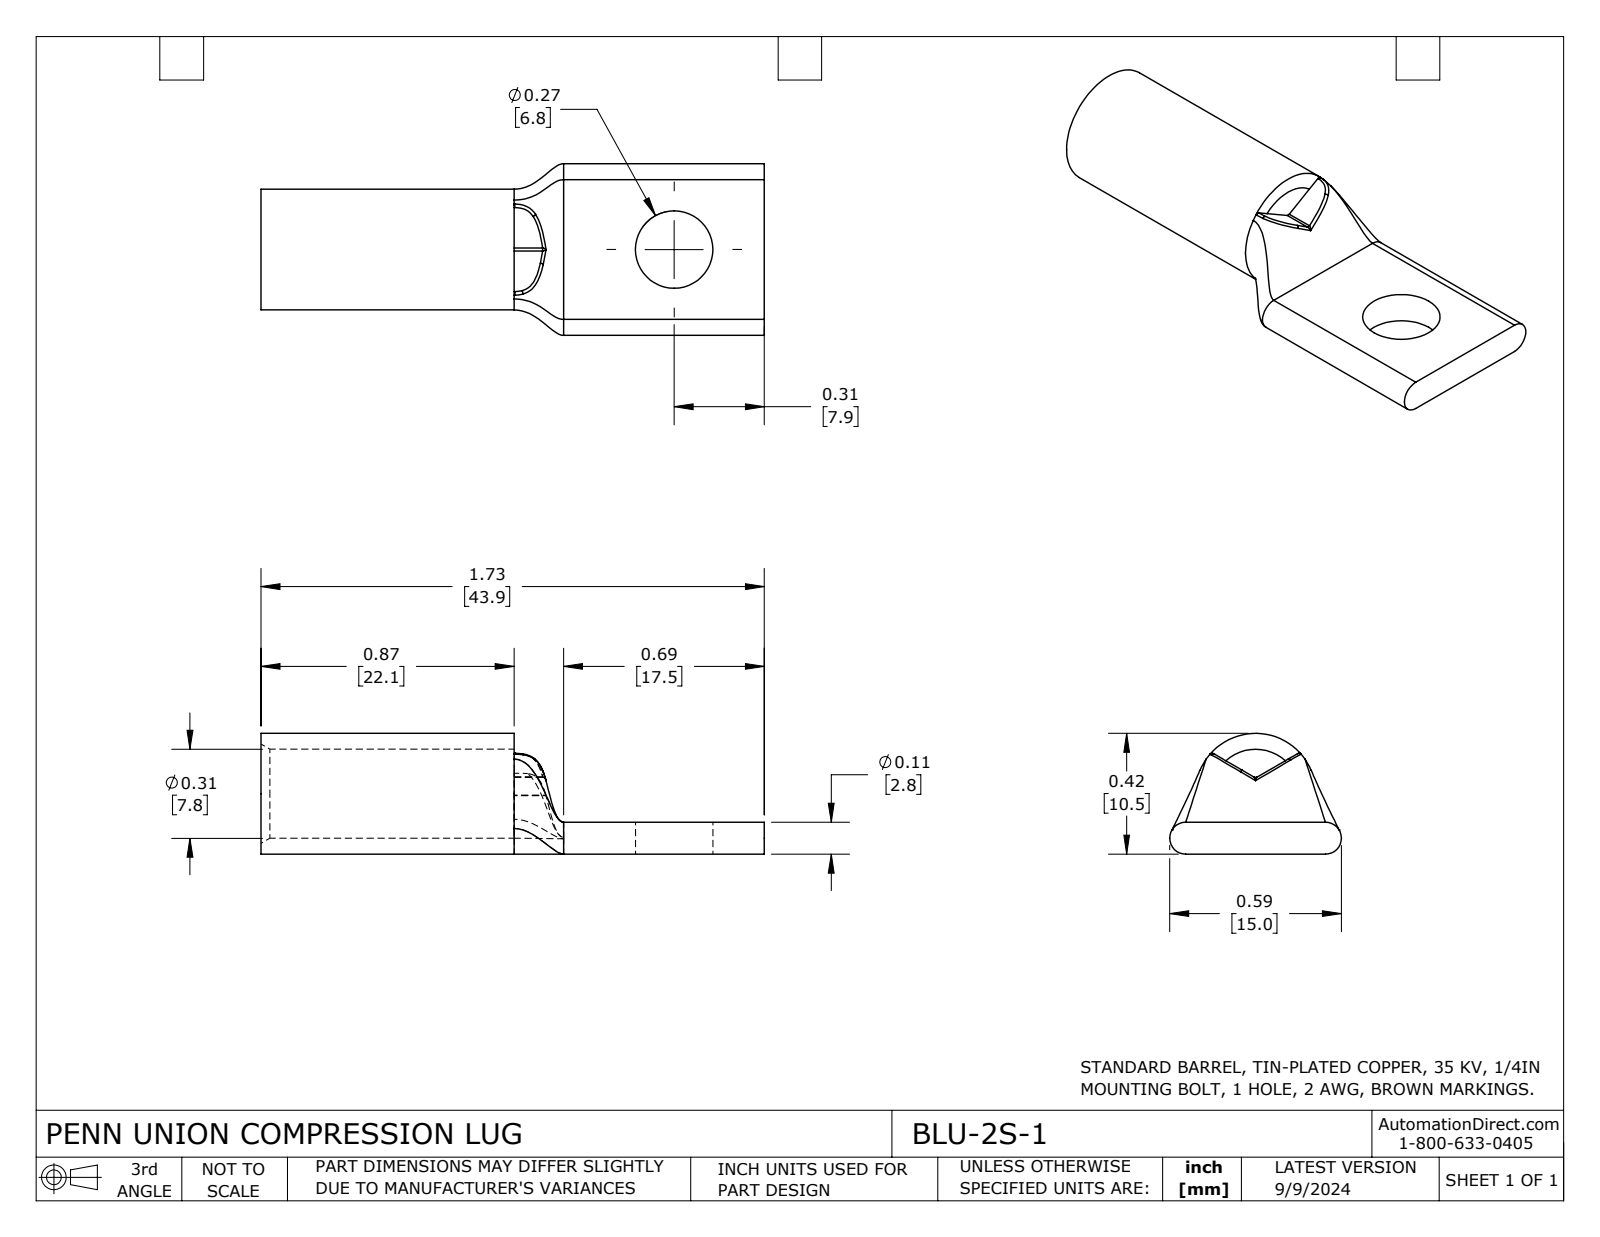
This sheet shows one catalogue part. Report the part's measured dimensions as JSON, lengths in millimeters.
{"part_name": "BLU-2S-1", "step_written_by": "SolidWorks 2023 (CONFIG_CONTROL_DESIGN)", "units": "millimeters", "bodies": {"solids": 1, "faces": 40, "planar": 11, "cylindrical": 11, "other": 18}, "overall_size": [43.9, 15, 10.5], "volume_mm3": 1660, "surface_area_mm2": 2262, "round_holes": [[6.8, 1], [7.8, 1]], "round_bosses_or_shafts": [[10.5, 1]], "partial_cylinders_radius": [[0.3, 2], [1.4, 2]], "face_to_face_distances": [2.8, 43.9, 22.1, 21.8, 1.4, 26.4, 4.3, 17.5]}
